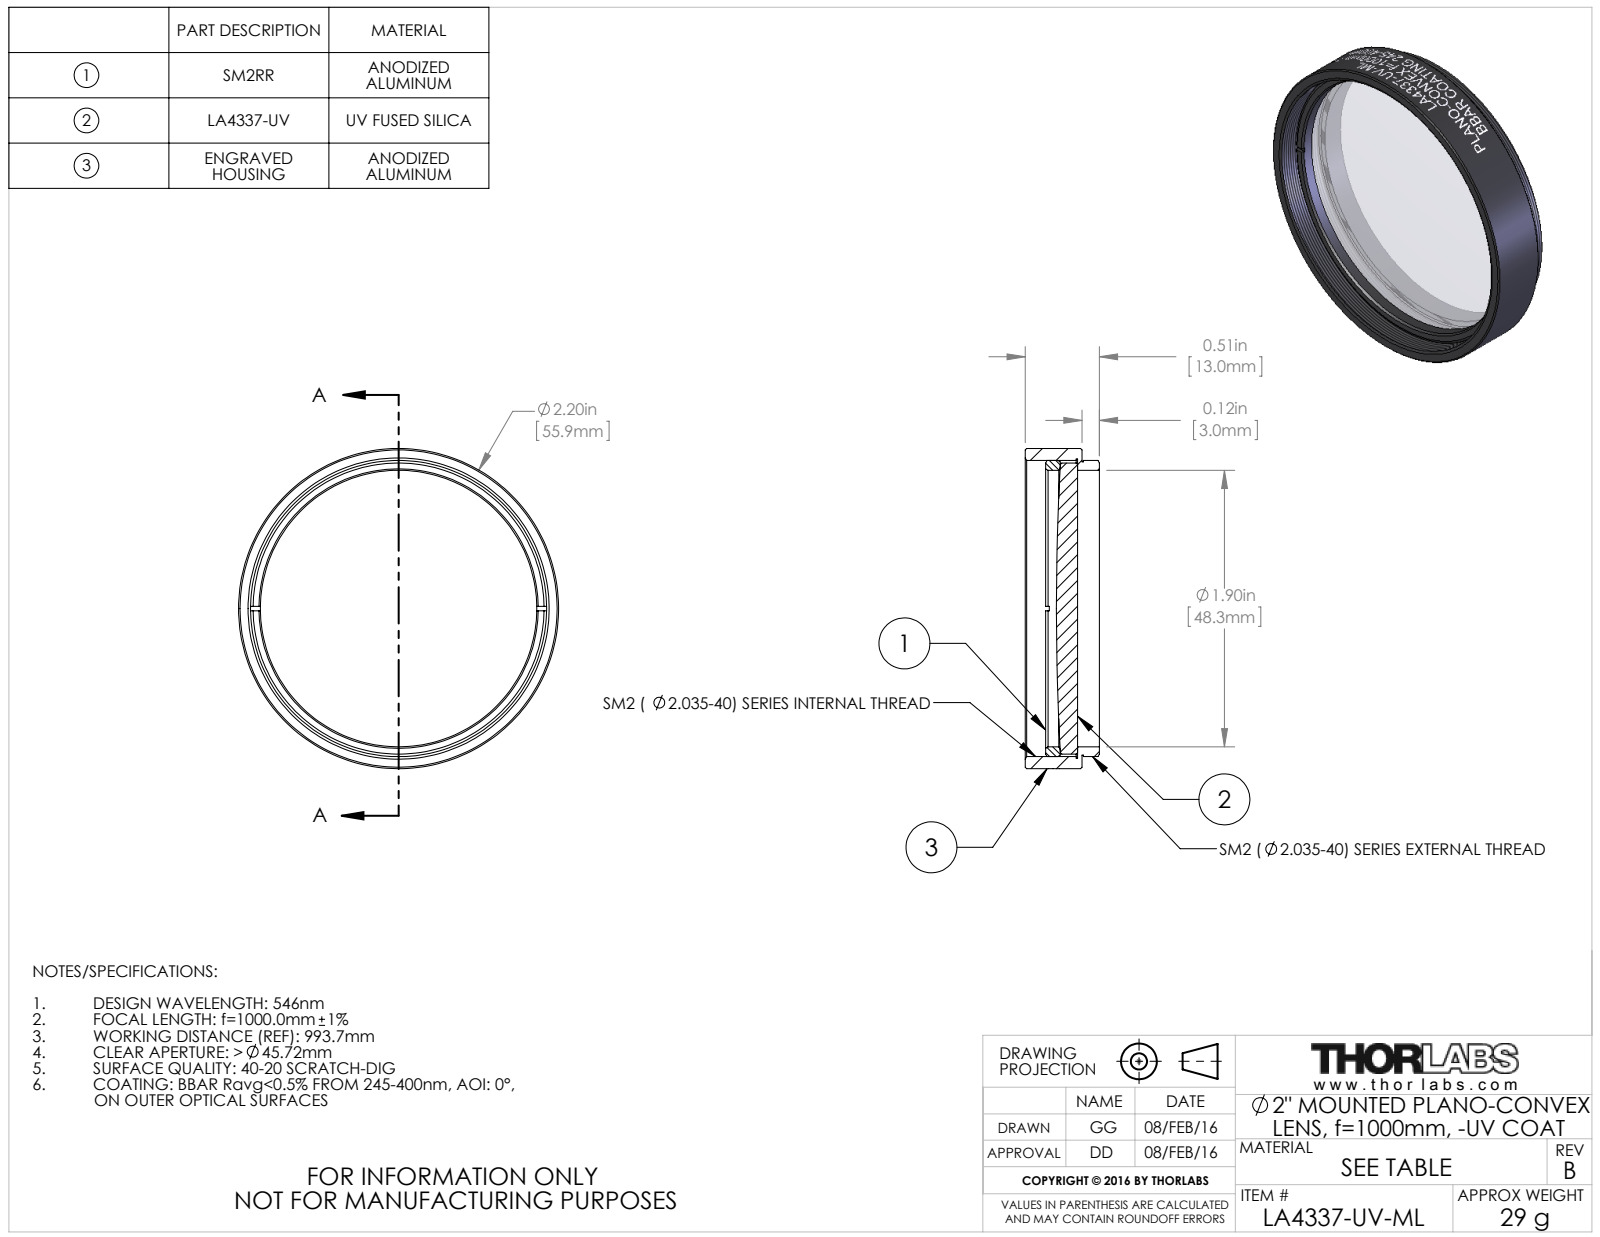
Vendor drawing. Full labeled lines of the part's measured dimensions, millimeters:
Part name (STEP PRODUCT): TTN039251-E0W
STEP written by: SolidWorks 2014 (CONFIG_CONTROL_DESIGN)
Units: millimetres
Bodies: 3 solids, 149 faces (16 planar, 109 cylindrical, 24 other)
Overall size (bounding box): 55.88 × 55.88 × 12.95
Volume: 11 909 mm³ · Surface area: 11 305 mm²
Round holes (diameter × count): ⌀48.26 ×1, ⌀52.2 ×1
Round bosses / shafts (diameter × count): ⌀55.88 ×1, ⌀51.69 ×1, ⌀51.18 ×1, ⌀50.8 ×1
Main face-to-face distances: 3.05, 3.81, 0.76, 9.91, 9.15, 12.96, 6.86, 6.1, 9.4, 6.35
